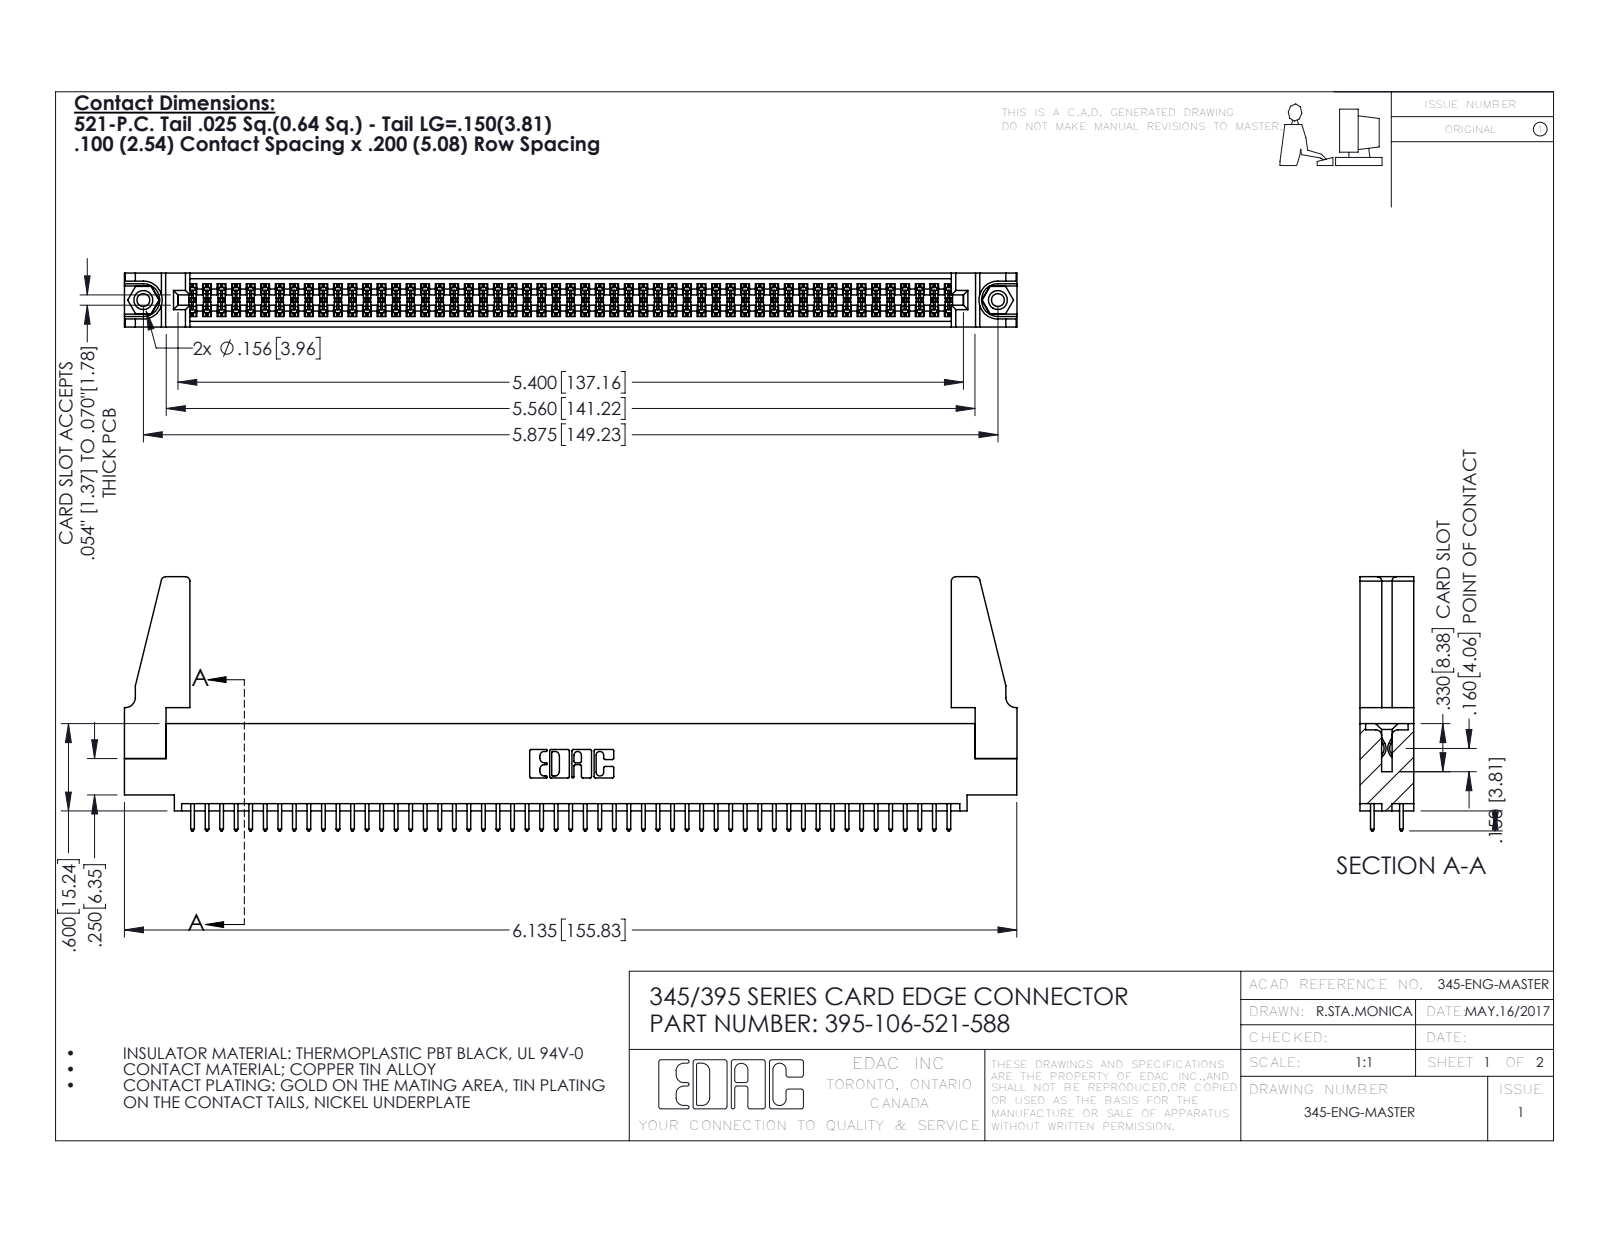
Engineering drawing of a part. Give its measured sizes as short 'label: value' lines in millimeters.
name: 395-106-521-588; 345 Part_0.110 Offset - 0.156 Dia-TH; 345-292-001_345-293-121; 345-250-001_345-250-001-102 (+1 more)
written by: SolidWorks 2016 (CONFIG_CONTROL_DESIGN)
unit: mm
bodies: 111 solids, 5554 faces (3654 planar, 1884 cylindrical, 16 other)
size: 155.9 × 44.4 × 9.4
volume: 18 370 mm³; area: 25 500 mm²
holes: 2× ⌀2.3, 2× ⌀3.2, 2× ⌀4, 1× ⌀1.6
bosses: 2× ⌀3.9
rounds: 159× R0.2, 106× R0.3, 22× R0.3, 8× R0.8, 6× R0.2, 6× R0.8, 3× R0.7, 2× R0.4
face distances: 1.8, 7.6, 9.4, 5.1, 2.5, 6.9, 0.6, 5.7, 4.4, 3.8
hole spacings: 6.9, 143.2, 149.2
